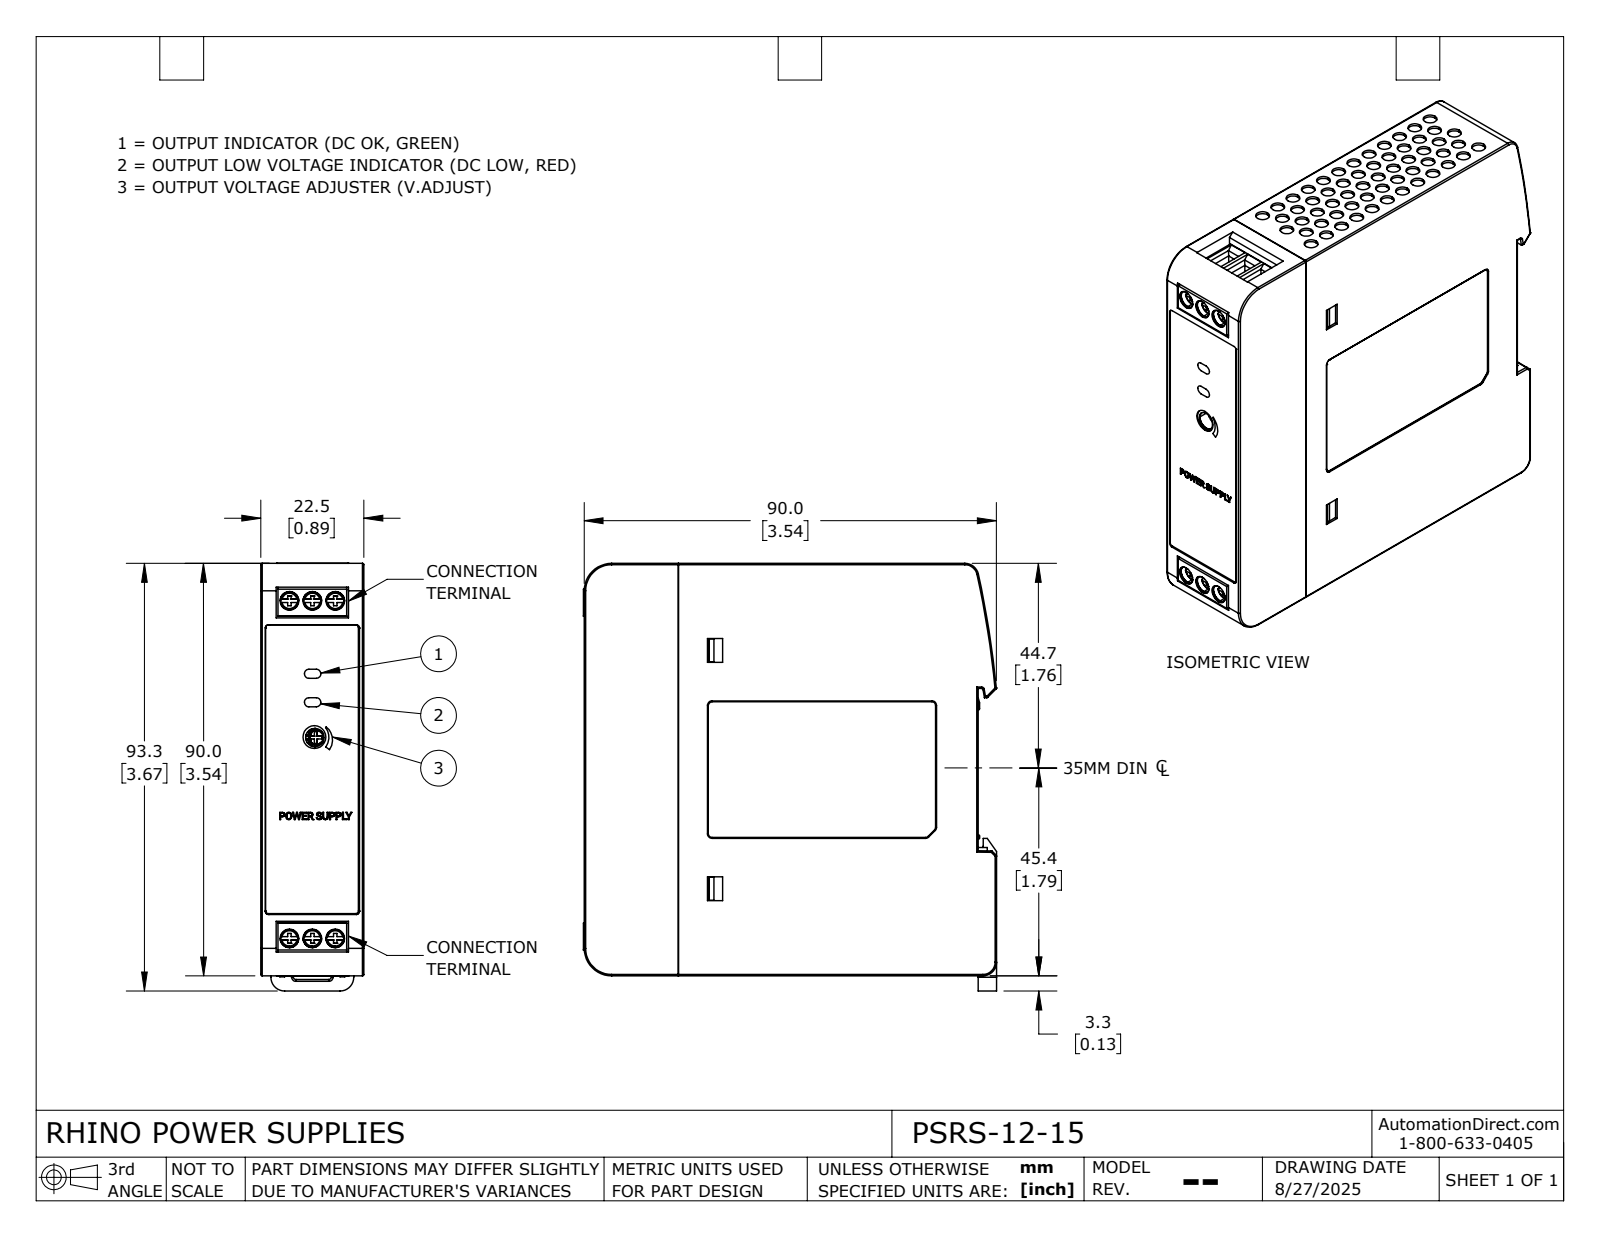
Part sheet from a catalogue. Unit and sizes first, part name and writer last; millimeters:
Units: millimetres
Overall size (bounding box): 93.3 × 90.17 × 22.5
Round holes (diameter × count): ⌀3.82 ×6, ⌀4.05 ×6, ⌀4 ×3, ⌀3.4 ×1
Round bosses / shafts (diameter × count): ⌀3.95 ×6, ⌀3 ×1, ⌀2 ×1
Partial cylindrical surfaces — rounded edges, fillets, slot ends (radius × count): R0.3 ×48, R1 ×11, R0.1 ×8, R3 ×8, R0.5 ×7, R2.5 ×3, R0.6 ×2, R1.1 ×2
Main face-to-face distances: 22.5, 22.35, 90, 85.85, 0.5, 89.5, 4, 2, 89.85, 15.3
Hole centre spacings: 5, 73.79, 73.62, 10, 29.82, 74.3, 6.2, 7.61
Volume: 174 150 mm³ · Surface area: 28 728 mm²
Bodies: 1 solid, 1156 faces (635 planar, 183 cylindrical, 338 other)
Part name (STEP PRODUCT): PSRS-12-15
STEP written by: SolidWorks 2024 (AUTOMOTIVE_DESIGN)
